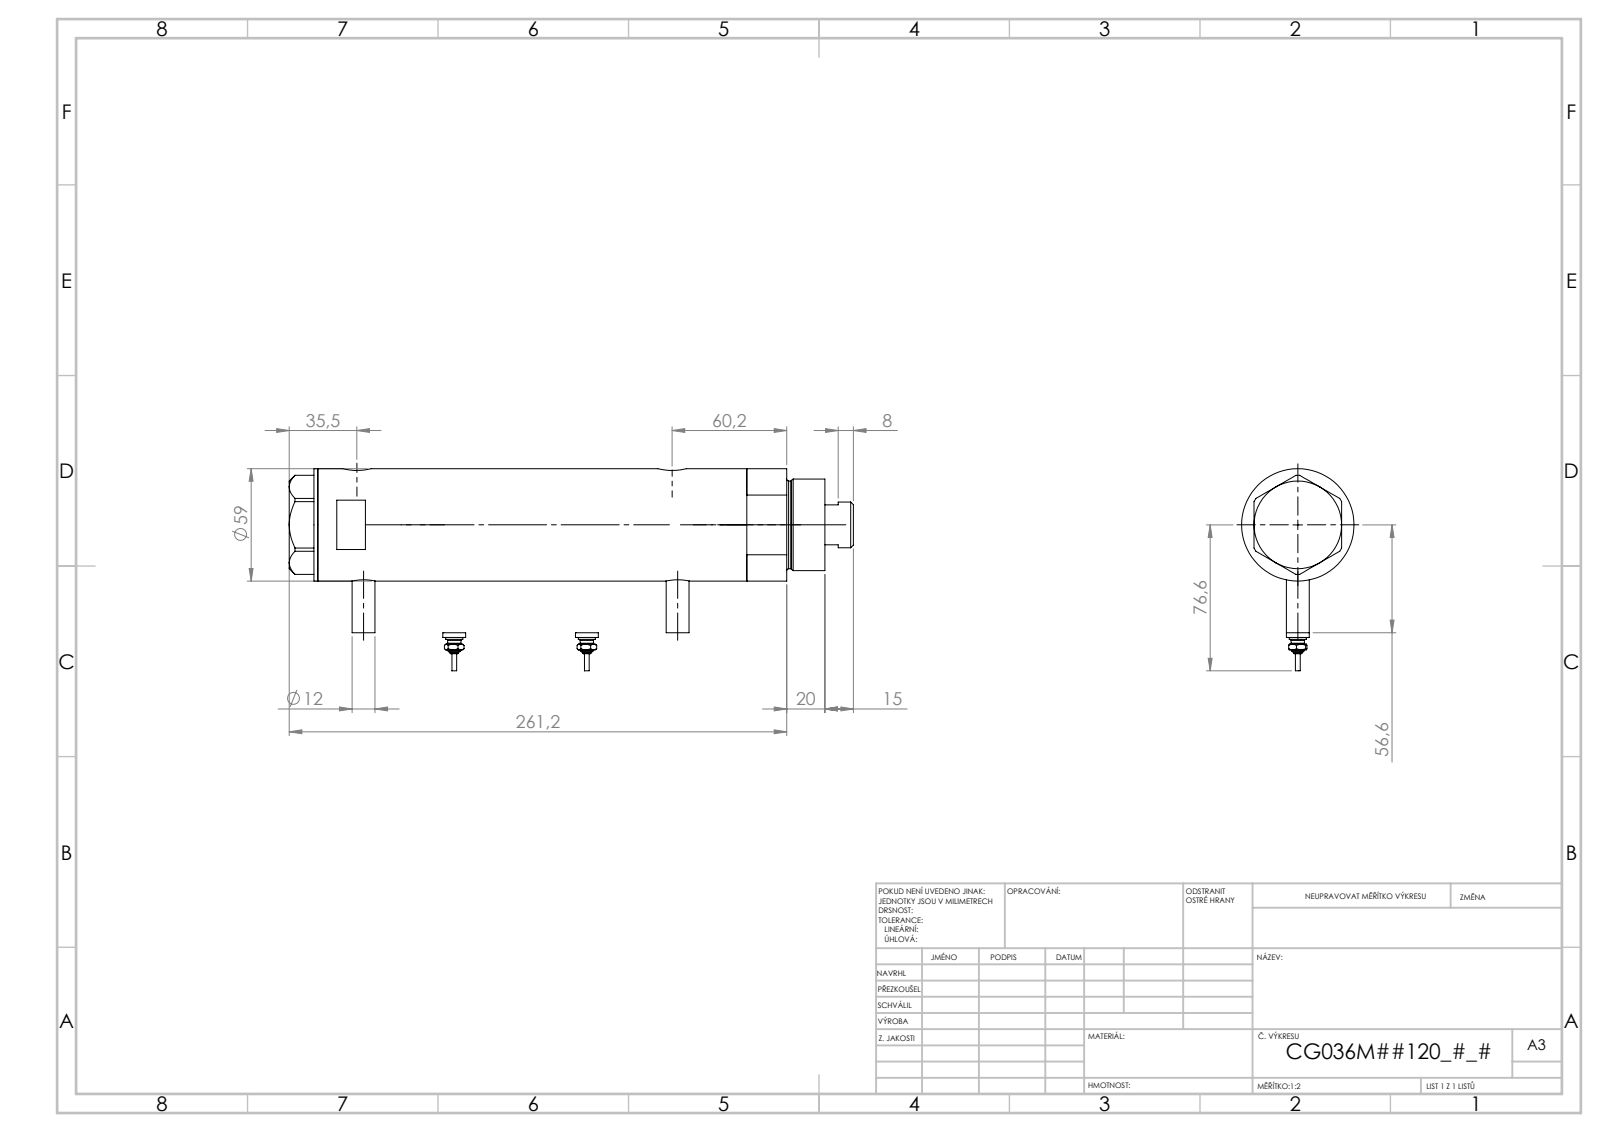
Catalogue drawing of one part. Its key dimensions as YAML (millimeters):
part_name: "V270CG_BACK; V270CG_VC; V270CG_SWITCH; V270CG_FRONT (+1 more)"
step_written_by: "SolidWorks 2019 (CONFIG_CONTROL_DESIGN)"
units: millimeters
bodies: {solids: 6, faces: 232, planar: 81, cylindrical: 77, other: 74}
overall_size: [283.42, 91.3, 59]
volume: 638834
surface_area: 129079
round_holes:
  - {diameter: 5, count: 2}
  - {diameter: 9.73, count: 2}
  - {diameter: 12.5, count: 2}
  - {diameter: 15, count: 2}
  - {diameter: 8.5, count: 1}
  - {diameter: 25, count: 1}
  - {diameter: 26.5, count: 1}
  - {diameter: 36, count: 1}
  - {diameter: 40, count: 1}
  - {diameter: 52, count: 1}
round_bosses_or_shafts:
  - {diameter: 12, count: 4}
  - {diameter: 9, count: 2}
  - {diameter: 7, count: 2}
  - {diameter: 4.34, count: 2}
  - {diameter: 2.4, count: 2}
  - {diameter: 59, count: 1}
  - {diameter: 48, count: 1}
  - {diameter: 46, count: 1}
face_to_face_distances: [177.34, 23.5, 153.84, 15, 38.5, 192.34, 268.42, 253.42, 229.92, 76.08]
hole_center_spacings: [2.9, 3.5, 152.15, 155.05, 155.65, 158.55, 2.89, 2.91]
